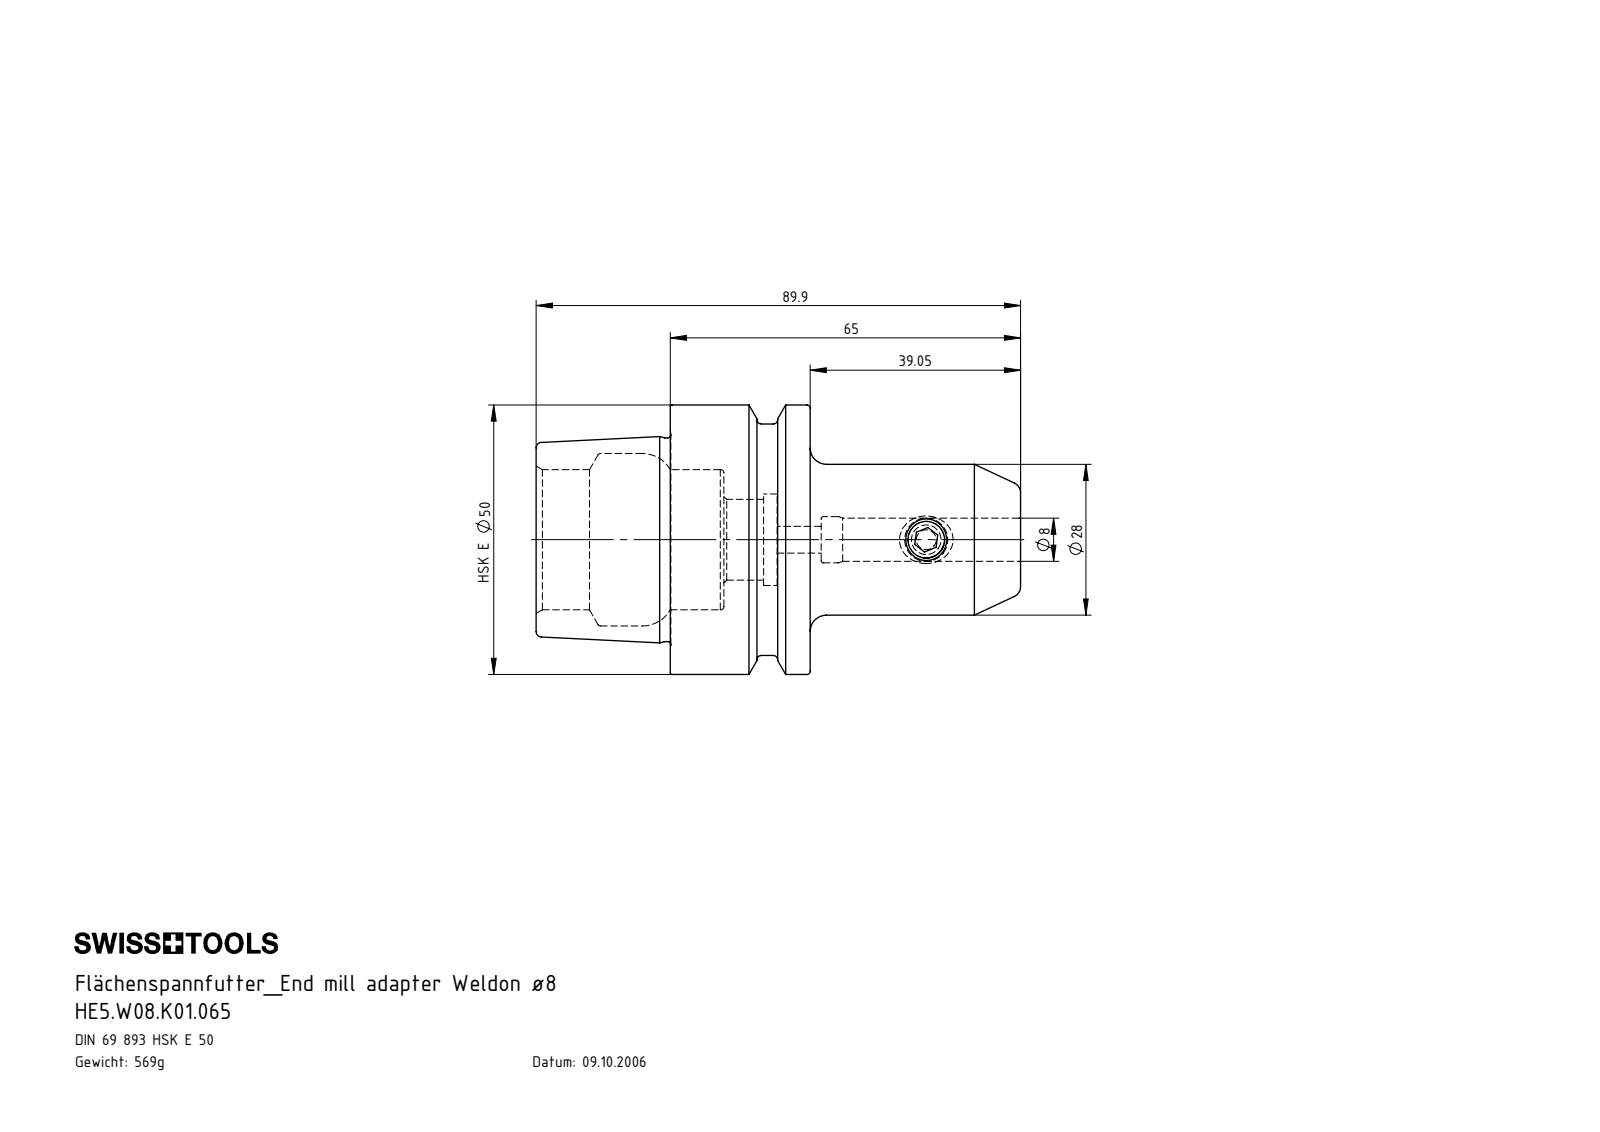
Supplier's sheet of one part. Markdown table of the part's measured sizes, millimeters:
| quantity | value |
| --- | --- |
| part name | W08-ER1.001.010; HE5-W08.K01.065_B_Fertigbearbeitung; HE5.W08.K01.065 |
| STEP written by | SolidWorks 2017 (AUTOMOTIVE_DESIGN) |
| units | millimeters |
| bodies | 2 solids, 109 faces (19 planar, 30 cylindrical, 60 other) |
| overall size | 89.9 × 50 × 50 |
| volume | 72 443 mm³ |
| surface area | 19 601 mm² |
| round holes (diameter × count) | 5 × 1, 6.8 × 1, 8 × 1, 8.6 × 1, 15 × 1, 17 × 1, 26 × 1, 32 × 1 |
| round bosses / shafts (diameter × count) | 50 × 1, 42.95 × 1, 37.81 × 1, 28 × 1, 8 × 1 |
| main face-to-face distances | 25.95, 24.9, 50.85, 34.85, 9.95, 16, 44.7, 19.8, 9.85, 6.15 |
